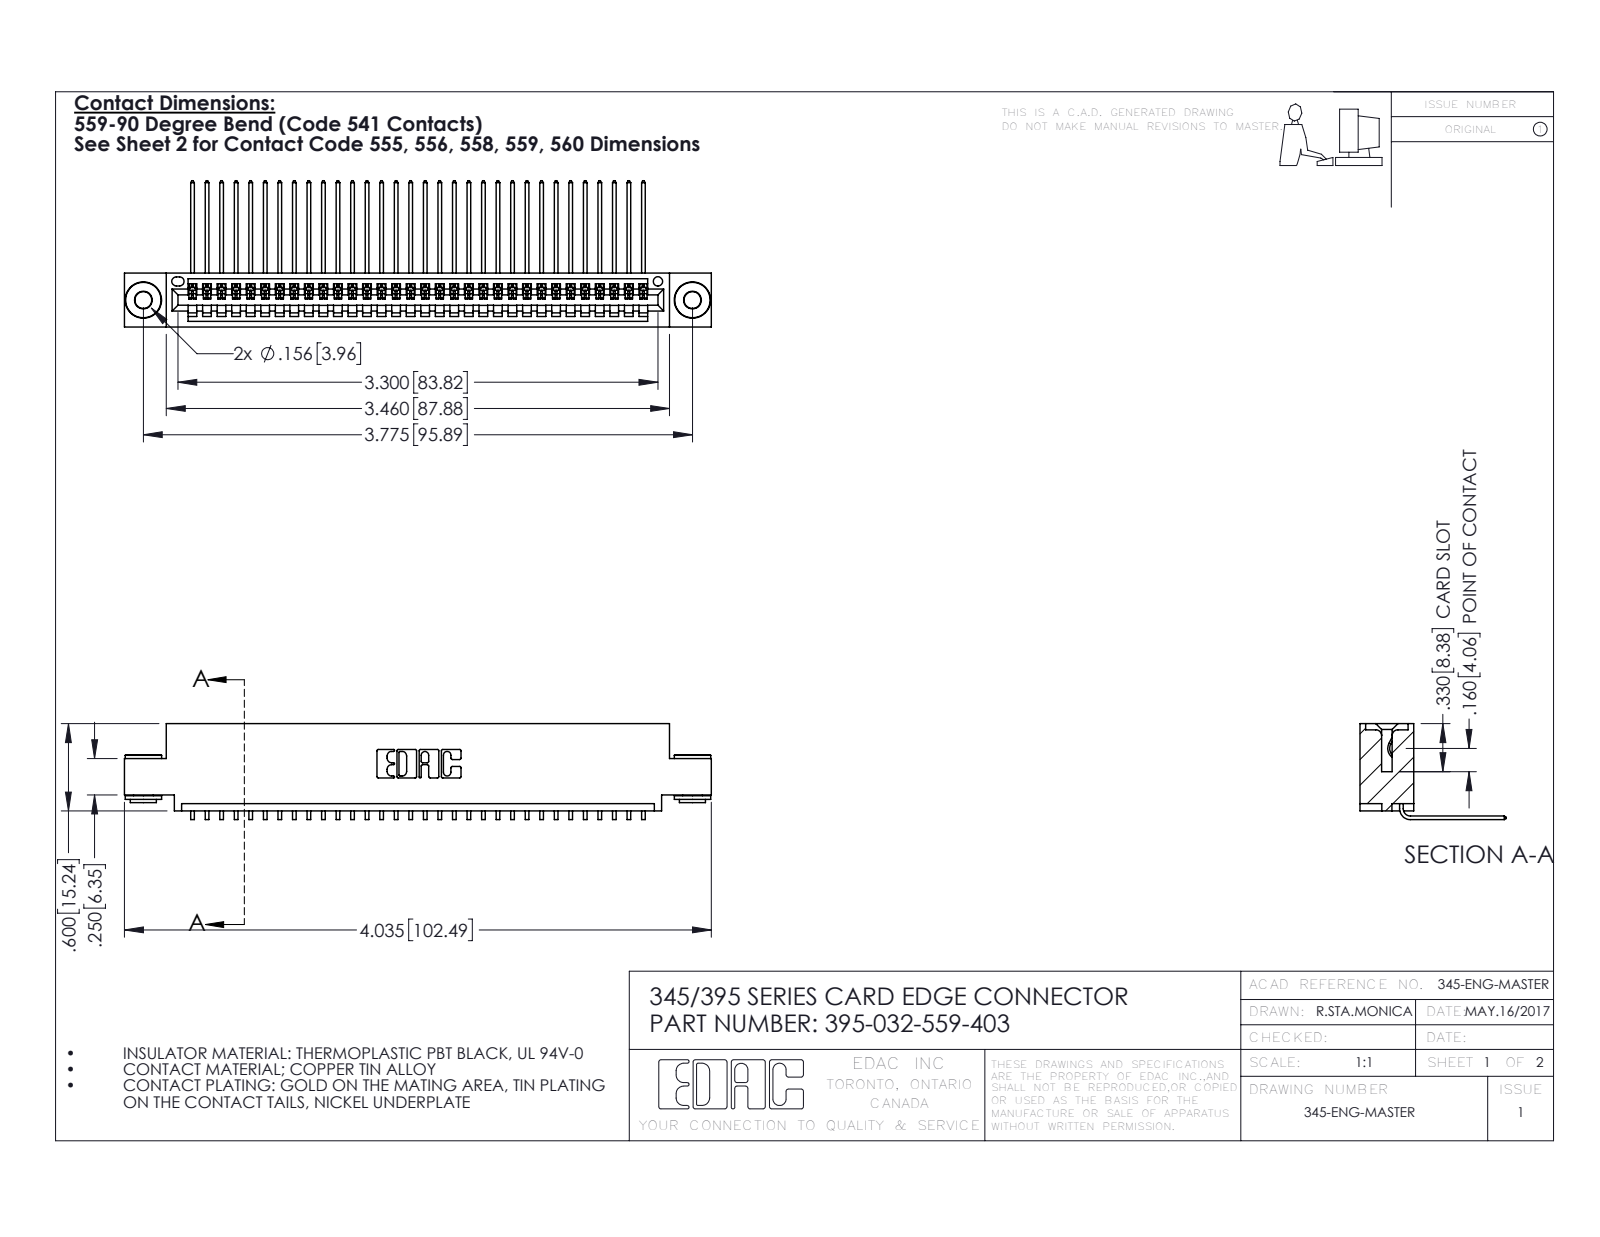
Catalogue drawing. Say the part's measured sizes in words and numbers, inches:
The part is named "345-292-001_558 559 Tail - 1; 395-032-559-403; 345 Part_0.110 Offset - 0.156 Dia-TH; 345-250-002_345-250-002-102". Its 3-D file was written by "SolidWorks 2016 (CONFIG_CONTROL_DESIGN)". It is 35 solids with 2088 faces: 1438 planar, 642 cylindrical and 8 other. Overall it measures 4.035 by 1.005 by 0.659 inches. Its volume is 0.592 cubic inches and its surface area 21.21 square inches. Round holes: 2 of diameter 0.116, 2 of diameter 0.156, 1 of diameter 0.064. Round bosses or shafts: 2 of diameter 0.25, 2 of diameter 0.18, 2 of diameter 0.136. Partial cylindrical surfaces (rounded edges, fillets, slot ends): 64 of radius 0.006, 22 of radius 0.01, 6 of radius 0.007, 6 of radius 0.031, 3 of radius 0.026, 2 of radius 0.031, 2 of radius 0.04, 1 of radius 0.014. The main face-to-face distances are 0.072, 0.298, 0.37, 0.2, 0.025, 0.098, 0.272, 0.225, 0.149, 0.072. The hole center spacings are 0.27, 3.54, 3.775.
